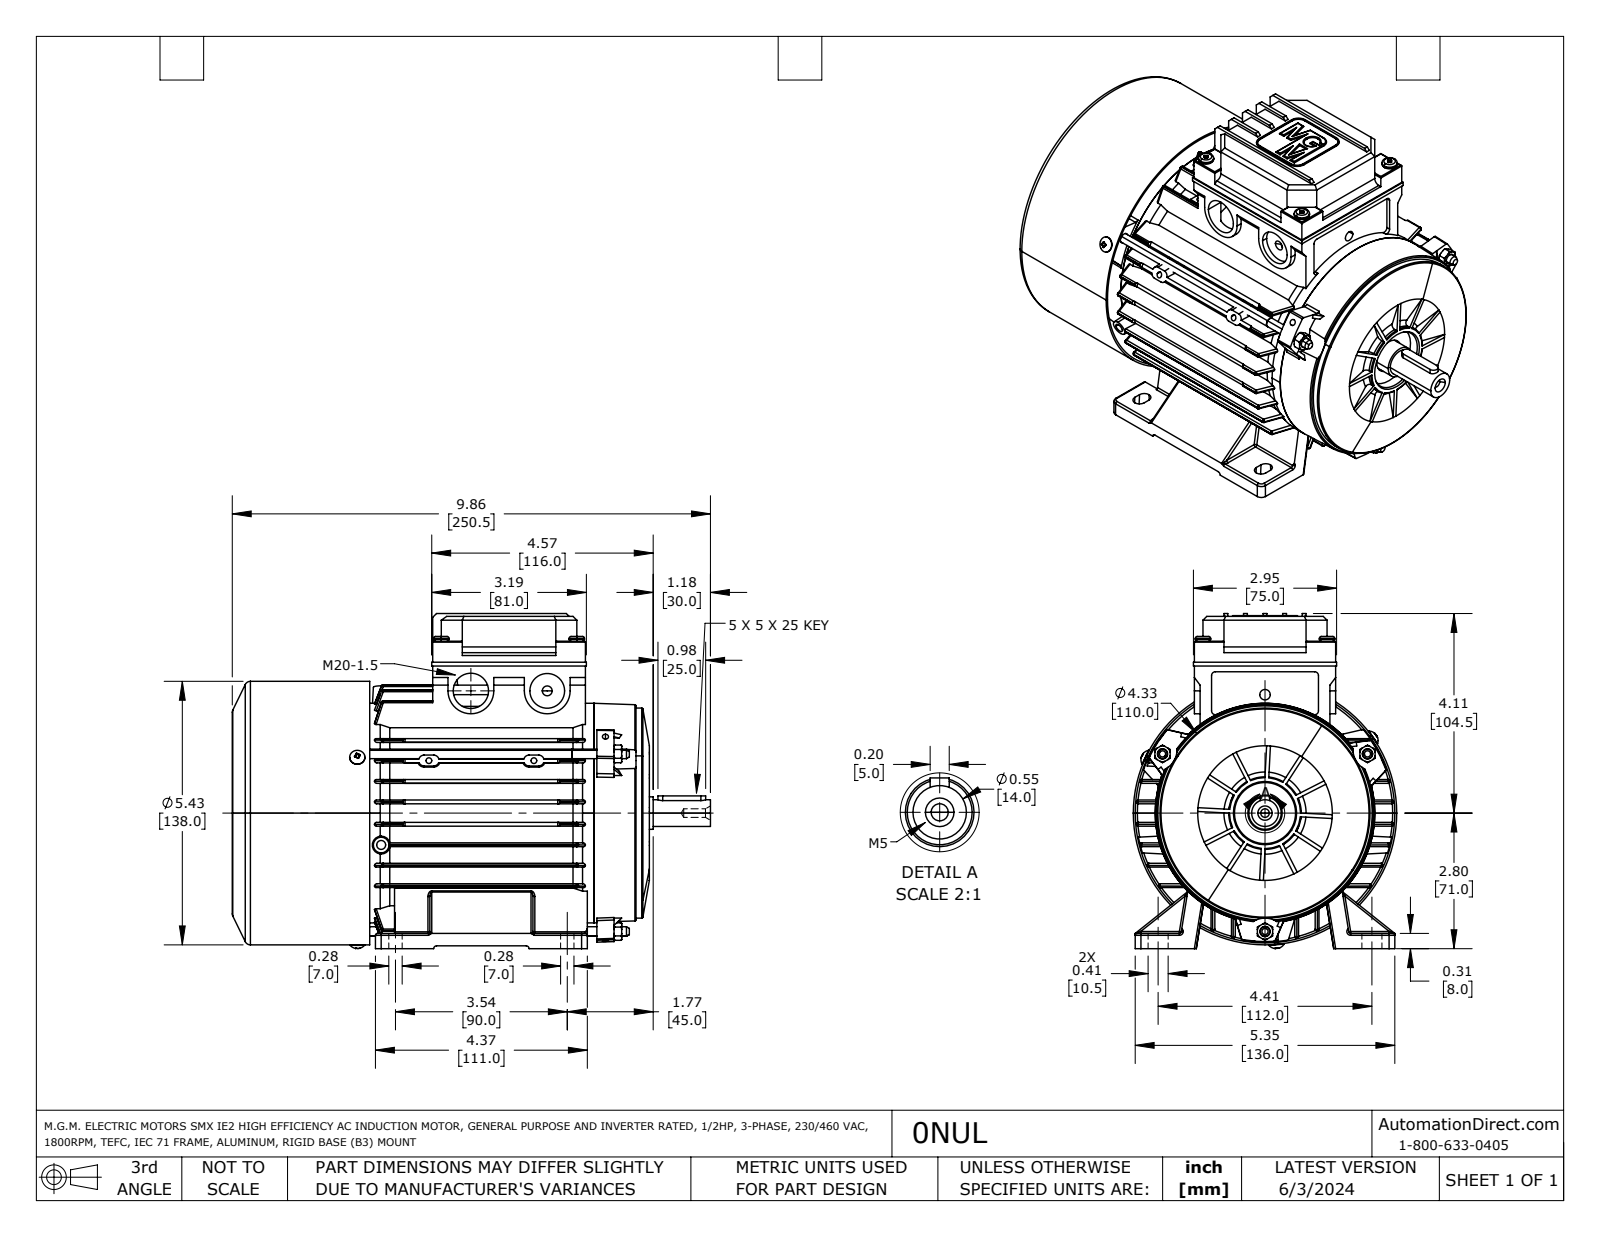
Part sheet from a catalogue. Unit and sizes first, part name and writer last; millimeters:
Units: millimetres
Overall size (bounding box): 250.5 × 175.5 × 138
Round holes (diameter × count): ⌀3 ×14, ⌀5.5 ×8, ⌀3.3 ×7, ⌀3.2 ×6, ⌀4 ×4, ⌀4.5 ×4, ⌀7 ×3, ⌀4.7 ×2, ⌀8 ×1, ⌀18 ×1, ⌀18.2 ×1, ⌀18.5 ×1
Round bosses / shafts (diameter × count): ⌀3 ×10, ⌀8 ×7, ⌀3.5 ×4, ⌀5 ×3, ⌀2 ×3, ⌀138 ×1, ⌀115 ×1, ⌀112.3 ×1
Partial cylindrical surfaces — rounded edges, fillets, slot ends (radius × count): R1 ×316, R0.9 ×56, R0.4 ×36, R0.2 ×32, R0.5 ×30, R0.1 ×16, R0.8 ×16, R3 ×12
Main face-to-face distances: 2, 10.7, 43.8, 21.4, 33.1, 8.7, 12.7, 54.6, 22.4, 45.8
Hole centre spacings: 12.1, 62, 14.5, 19, 28, 31, 31, 39.6
Volume: 564 400 mm³ · Surface area: 434 500 mm²
Bodies: 24 solids, 3315 faces (1040 planar, 1121 cylindrical, 1154 other)
Part name (STEP PRODUCT): 0NUL
STEP written by: SolidWorks 2021 (AUTOMOTIVE_DESIGN)
